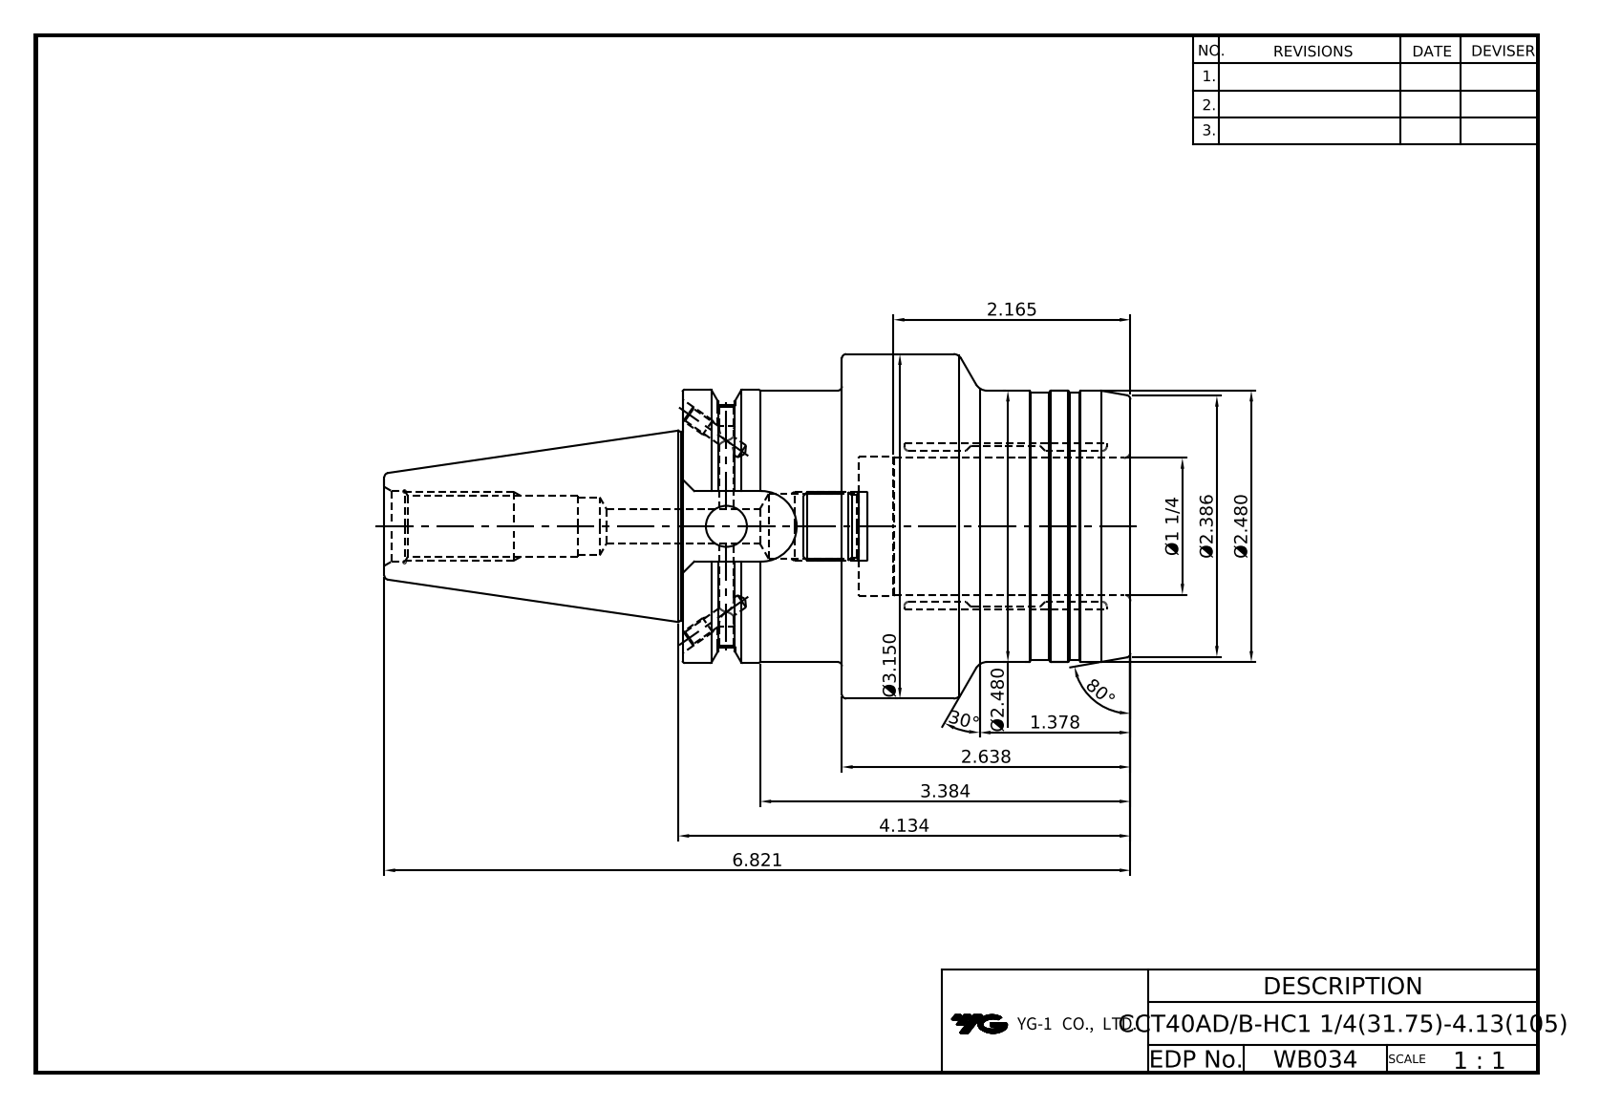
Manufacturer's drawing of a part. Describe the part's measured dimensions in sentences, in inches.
The part is named "CCT40ADB-HC31.75-105". Its 3-D file was written by "Autodesk Inventor 2020 (AUTOMOTIVE_DESIGN)". It is 1 solid with 118 faces: 40 planar, 38 cylindrical and 40 other. Overall it measures 6.821 by 3.15 by 3.15 inches. Its volume is 22.79 cubic inches and its surface area 76.95 square inches. Round holes: 4 of diameter 0.128, 2 of diameter 0.157, 2 of diameter 0.165, 1 of diameter 0.315, 1 of diameter 0.375, 1 of diameter 0.512, 1 of diameter 0.527, 1 of diameter 0.587, 1 of diameter 0.642, 1 of diameter 1.25, 1 of diameter 1.283. Round bosses or shafts: 1 of diameter 3.15, 1 of diameter 2.5, 1 of diameter 2.48, 1 of diameter 2.441, 1 of diameter 1.724. Partial cylindrical surfaces (rounded edges, fillets, slot ends): 1 of radius 0.322, 1 of radius 1.108. The main face-to-face distances are 2.638, 1.457, 4.094, 1.614, 0.157, 2.48, 1.874, 0.645, 2.726, 4.183.
